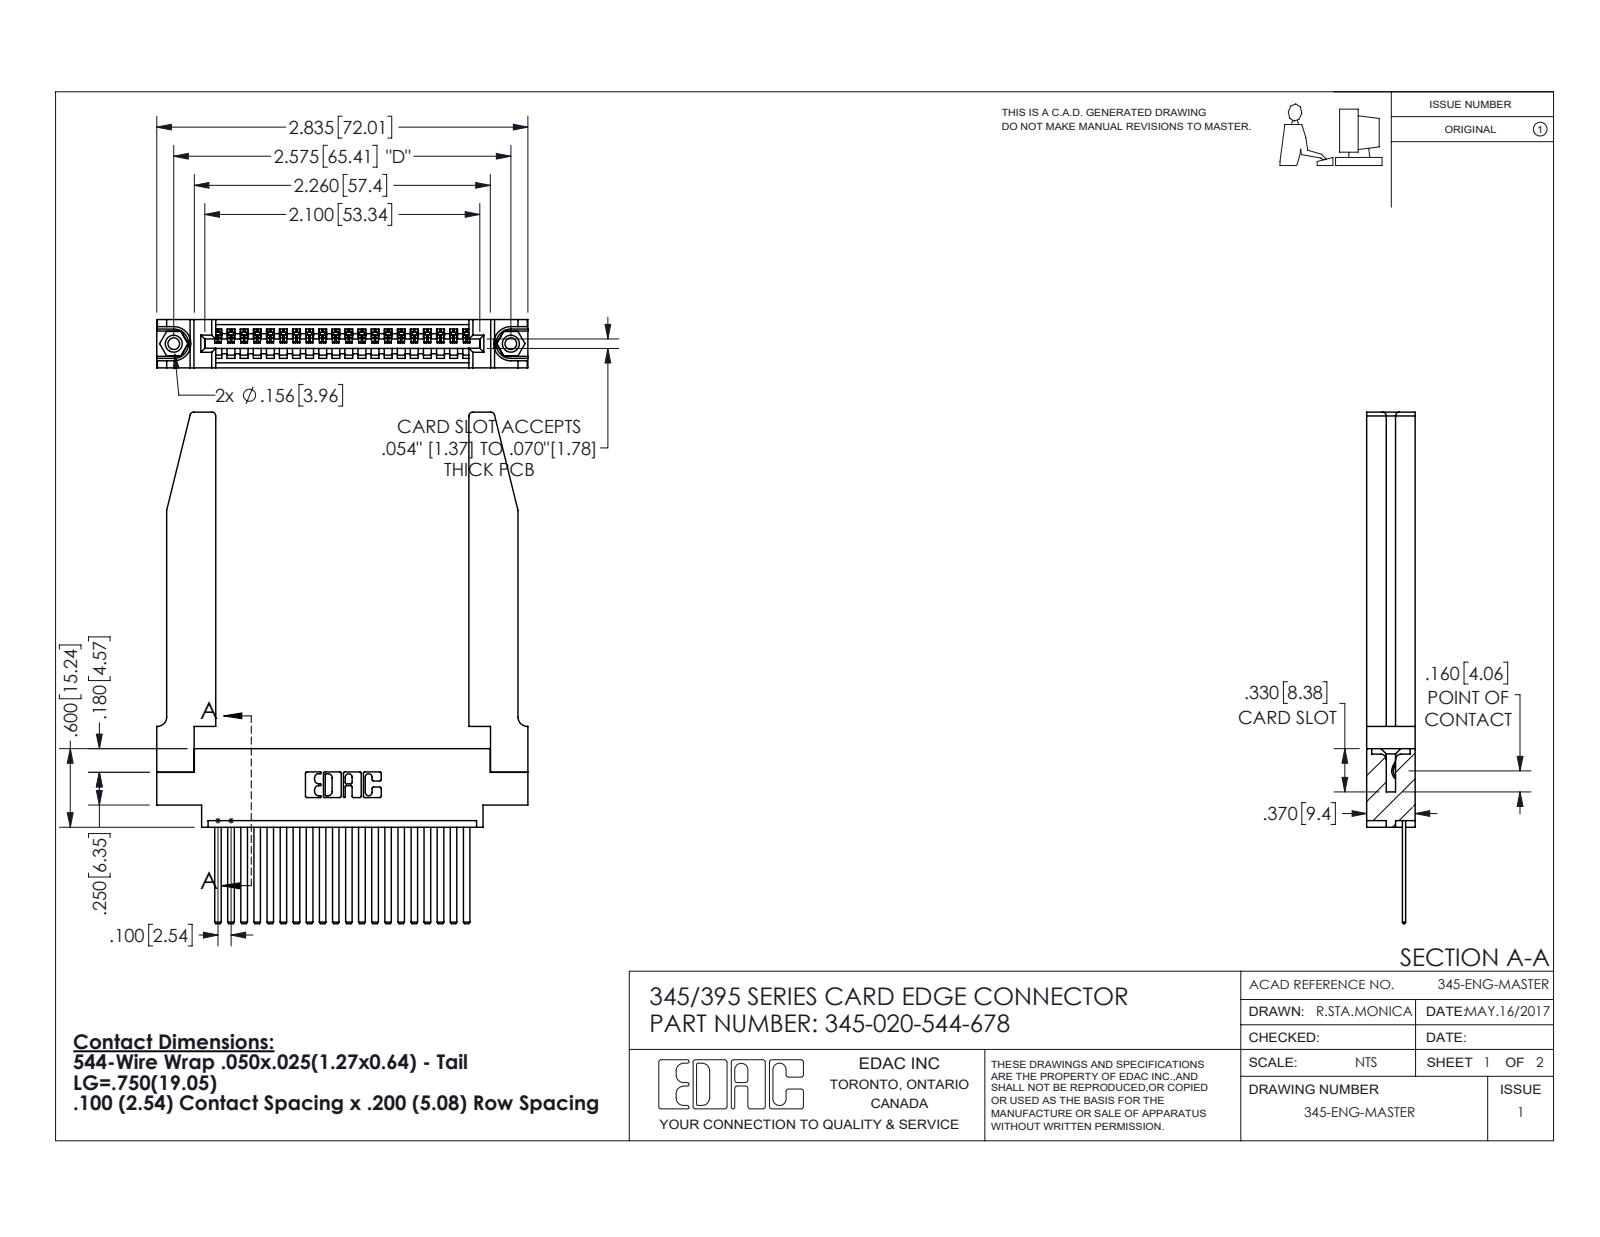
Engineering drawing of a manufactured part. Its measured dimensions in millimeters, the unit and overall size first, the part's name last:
Units: millimetres
Overall size (bounding box): 99.2 × 72 × 9.4
Round holes (diameter × count): ⌀2.3 ×2, ⌀3.2 ×2, ⌀4 ×2, ⌀1.6 ×1
Round bosses / shafts (diameter × count): ⌀3.9 ×2
Partial cylindrical surfaces — rounded edges, fillets, slot ends (radius × count): R0.2 ×40, R0.3 ×22, R0.8 ×8, R0.2 ×6, R0.8 ×6, R0.7 ×3, R0.8 ×2, R1 ×2
Main face-to-face distances: 9.4, 1.8, 7.6, 2.5, 6.9, 0.6, 5.1, 3.8, 3.8, 5.6
Hole centre spacings: 6.9, 59.5, 65.4
Volume: 14 600 mm³ · Surface area: 16 380 mm²
Bodies: 25 solids, 1404 faces (946 planar, 406 cylindrical, 52 other)
Part name (STEP PRODUCT): 345-220-078_345-220-078; 345-292-001_345-293-144; 345-020-544-678; 345 Part_0.170 Offset - 0.156 Dia-TH (+1 more)
STEP written by: SolidWorks 2016 (CONFIG_CONTROL_DESIGN)
